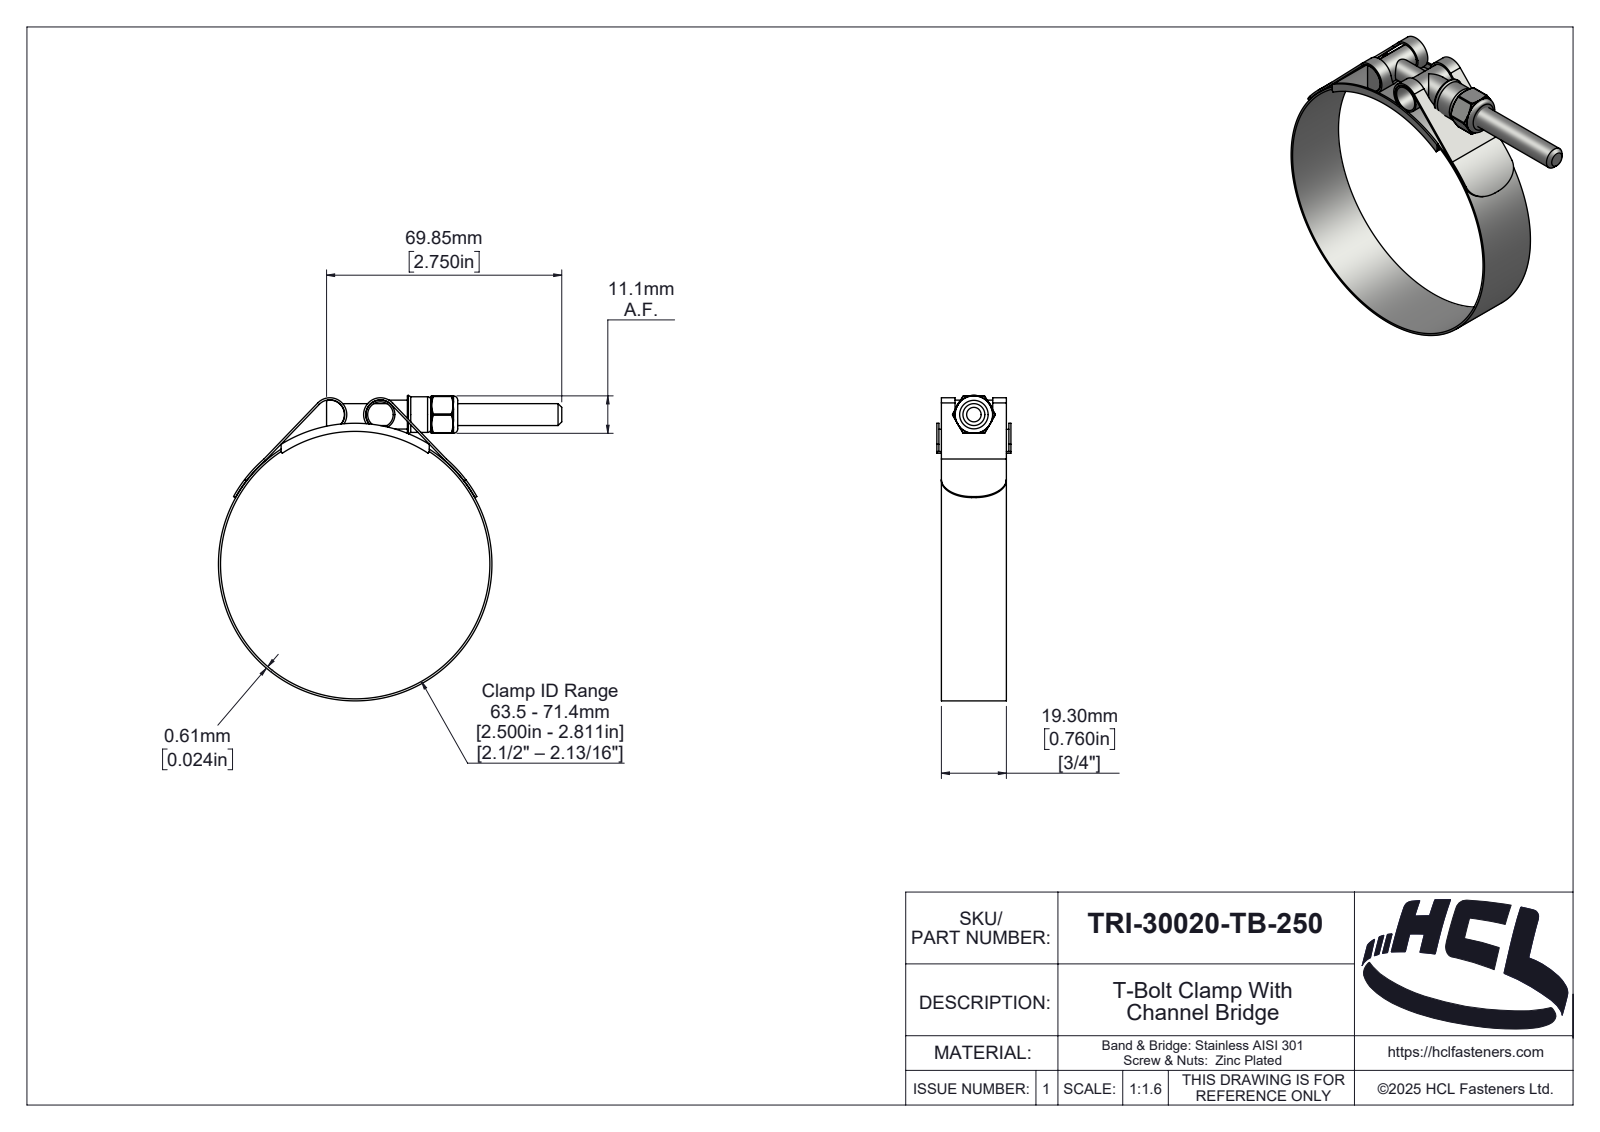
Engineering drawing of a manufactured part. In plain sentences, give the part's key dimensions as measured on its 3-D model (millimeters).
The part is named "TRI-30020-TB-250". Its 3-D file was written by "SolidWorks 2025 (AUTOMOTIVE_DESIGN)". It is 6 solids with 330 faces: 44 planar, 122 cylindrical and 164 other. Overall it measures 101.96 by 90.7 by 22 millimeters. Its volume is 8 660 cubic millimeters and its surface area 19 617 square millimeters. Round holes: 1 of diameter 5.4, 1 of diameter 6.35, 1 of diameter 6.5, 1 of diameter 7.58, 1 of diameter 80. Round bosses or shafts: 2 of diameter 8.58, 1 of diameter 81.22, 1 of diameter 10.58. Partial cylindrical surfaces (rounded edges, fillets, slot ends): 6 of radius 0.39, 2 of radius 0.5, 2 of radius 4.39, 2 of radius 5, 1 of radius 0.59, 1 of radius 2.42, 1 of radius 3.03, 1 of radius 3.19. The main face-to-face distances are 0.61, 19.3, 0.74, 1.35, 20.65, 21.39, 20.04, 22, 20.78, 31. The hole center spacings are 45.
